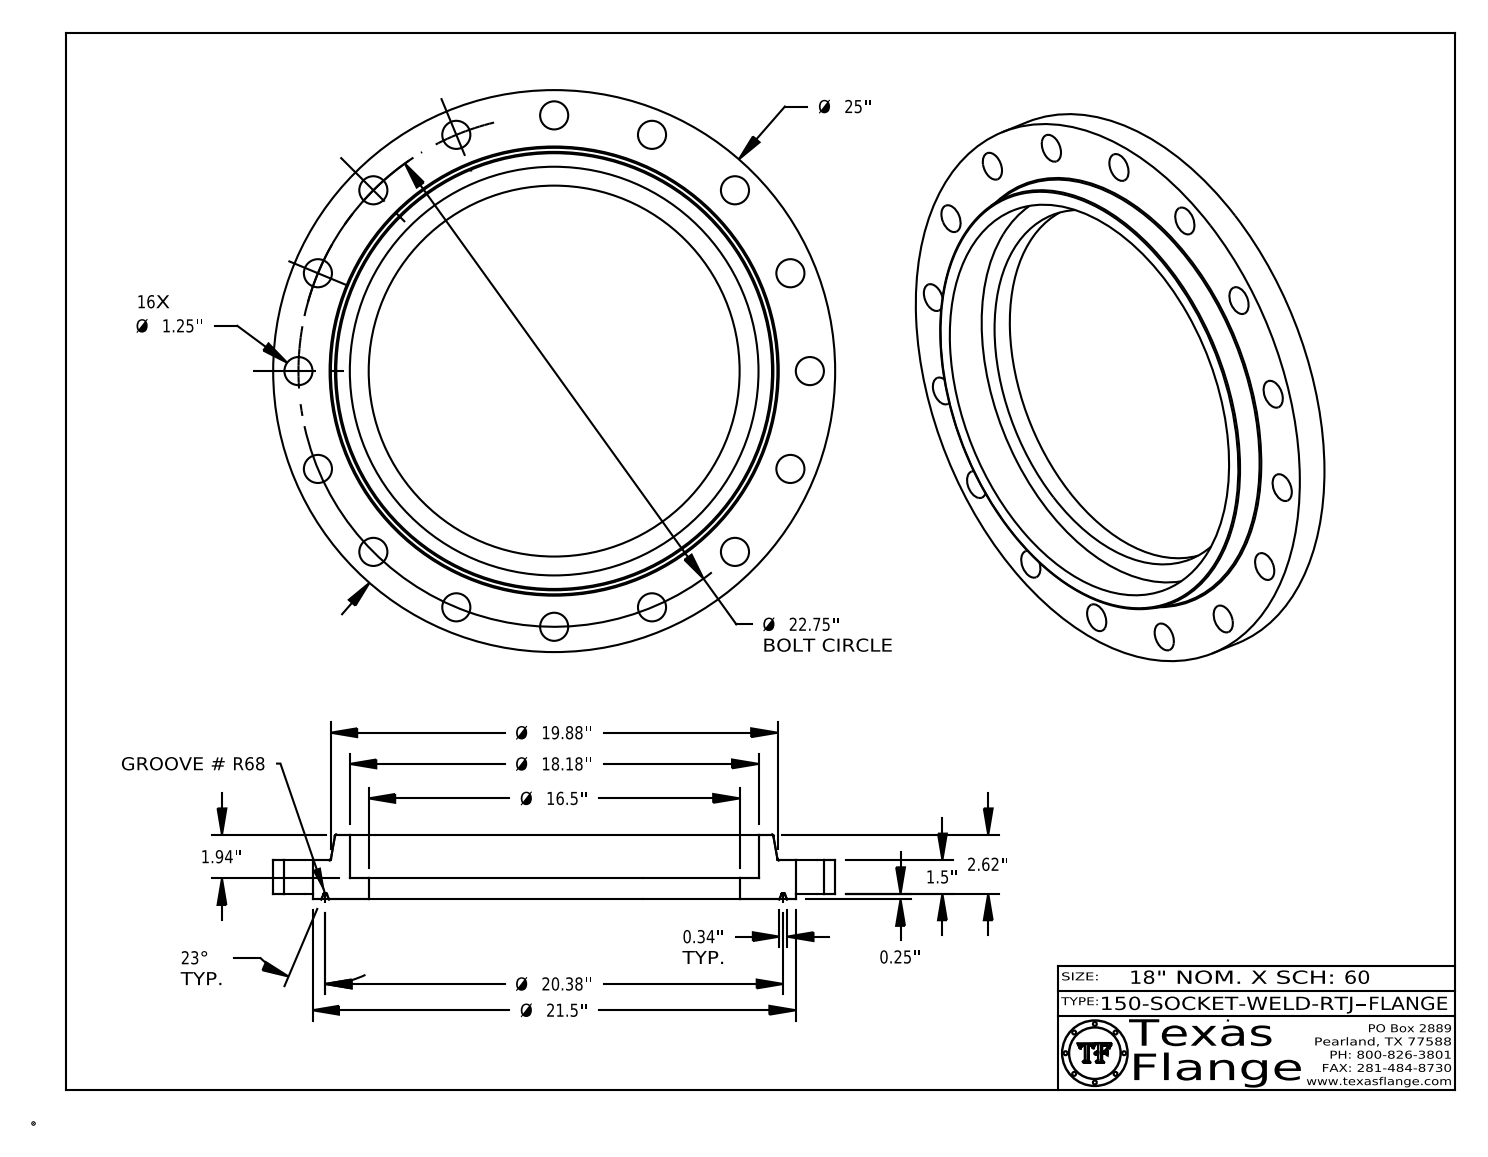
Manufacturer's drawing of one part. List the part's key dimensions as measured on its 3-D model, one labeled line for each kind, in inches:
Part name (STEP PRODUCT): 150-SOCKET-WELD-RTJ
STEP written by: CATIA V5 STEP AP214 (AUTOMOTIVE_DESIGN)
Units: inches
Bodies: 1 solid, 446 faces (372 planar, 60 cylindrical, 14 other)
Overall size (bounding box): 25 × 25 × 2.87
Volume: 432.2 in³ · Surface area: 979.5 in²
Round holes (diameter × count): ⌀1.25 ×16, ⌀0.495 ×1, ⌀16.5 ×1, ⌀18.18 ×1
Round bosses / shafts (diameter × count): ⌀0.03 ×8, ⌀25 ×1, ⌀21.5 ×1, ⌀0.39 ×1
Main face-to-face distances: 1.75, 0.25, 1.5, 0.93, 0.68, 0.82, 2.87, 2.62, 1.94, 1.12
Hole centre spacings: 12.639, 22.313, 11.375, 8.706, 16.087, 21.019, 4.438, 4.439
